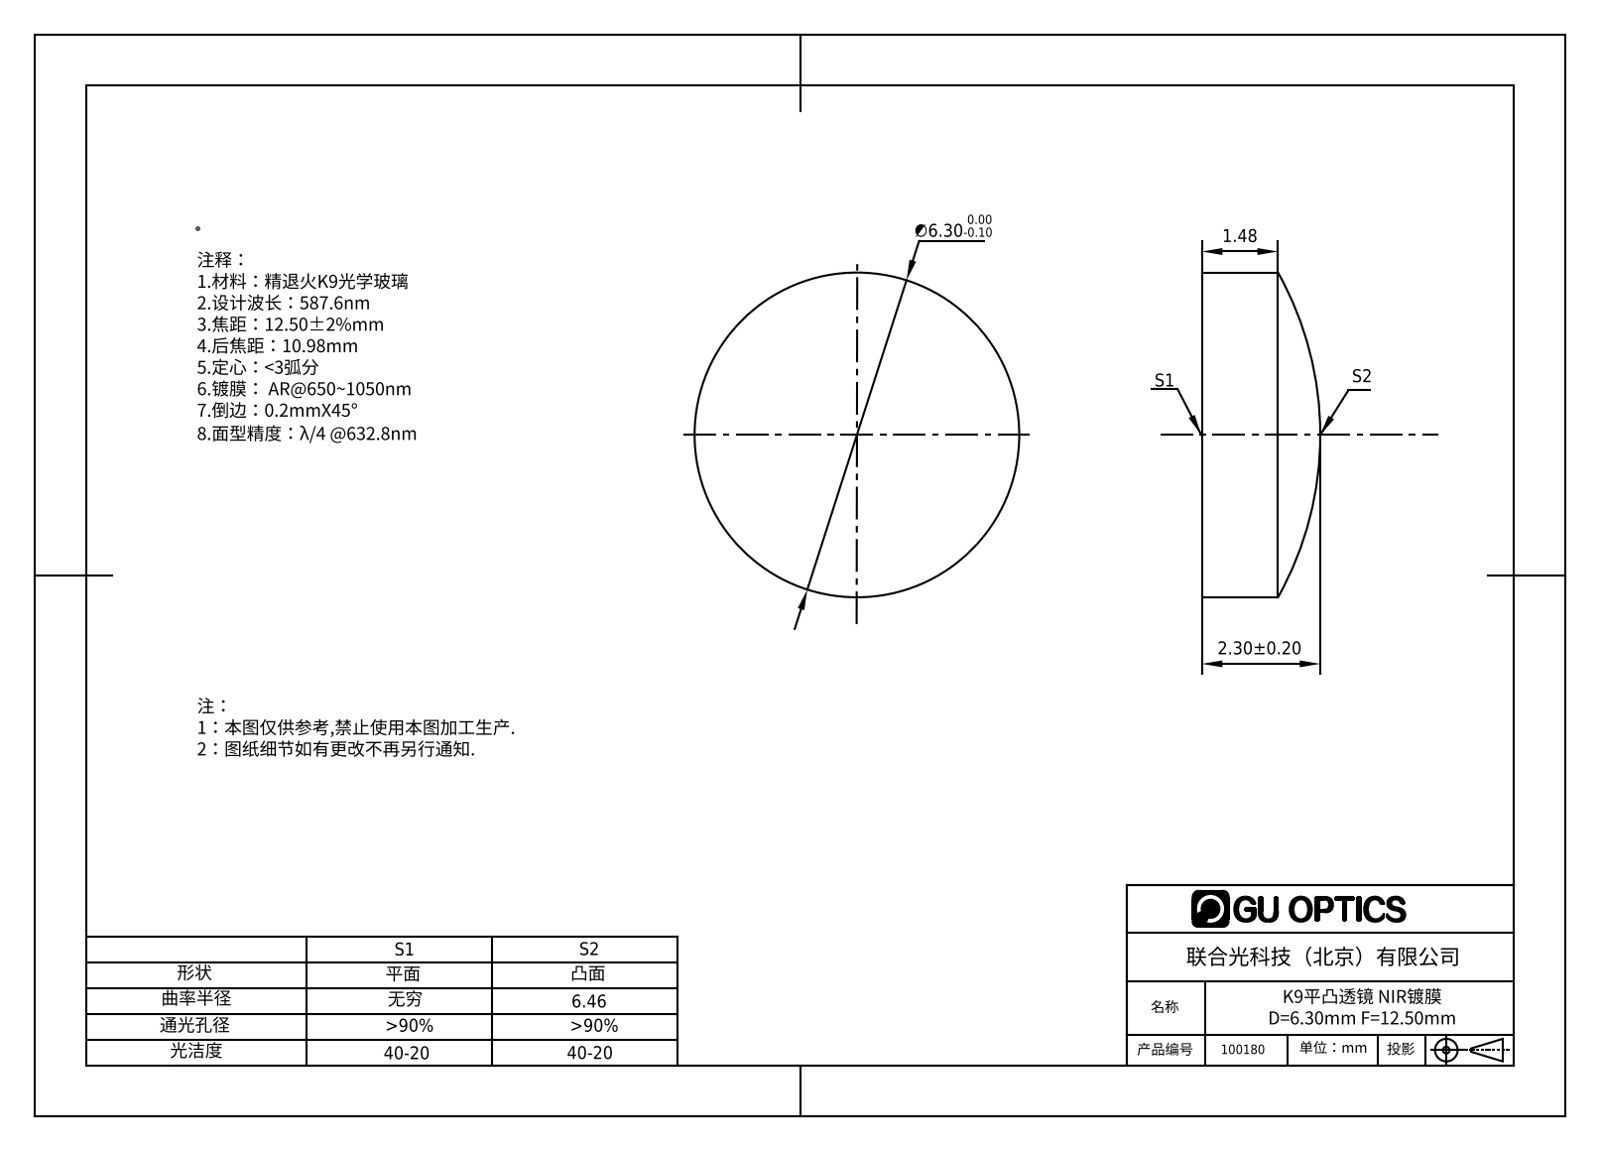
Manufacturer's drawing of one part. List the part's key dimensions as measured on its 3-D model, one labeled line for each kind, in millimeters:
Part name (STEP PRODUCT): 100180
STEP written by: SolidWorks 2016 (AUTOMOTIVE_DESIGN)
Units: millimetres
Bodies: 1 solid, 5 faces (1 planar, 2 cylindrical, 2 other)
Overall size (bounding box): 6.3 × 6.3 × 2.3
Volume: 59 mm³ · Surface area: 94 mm²
Round bosses / shafts (diameter × count): ⌀6.3 ×1
